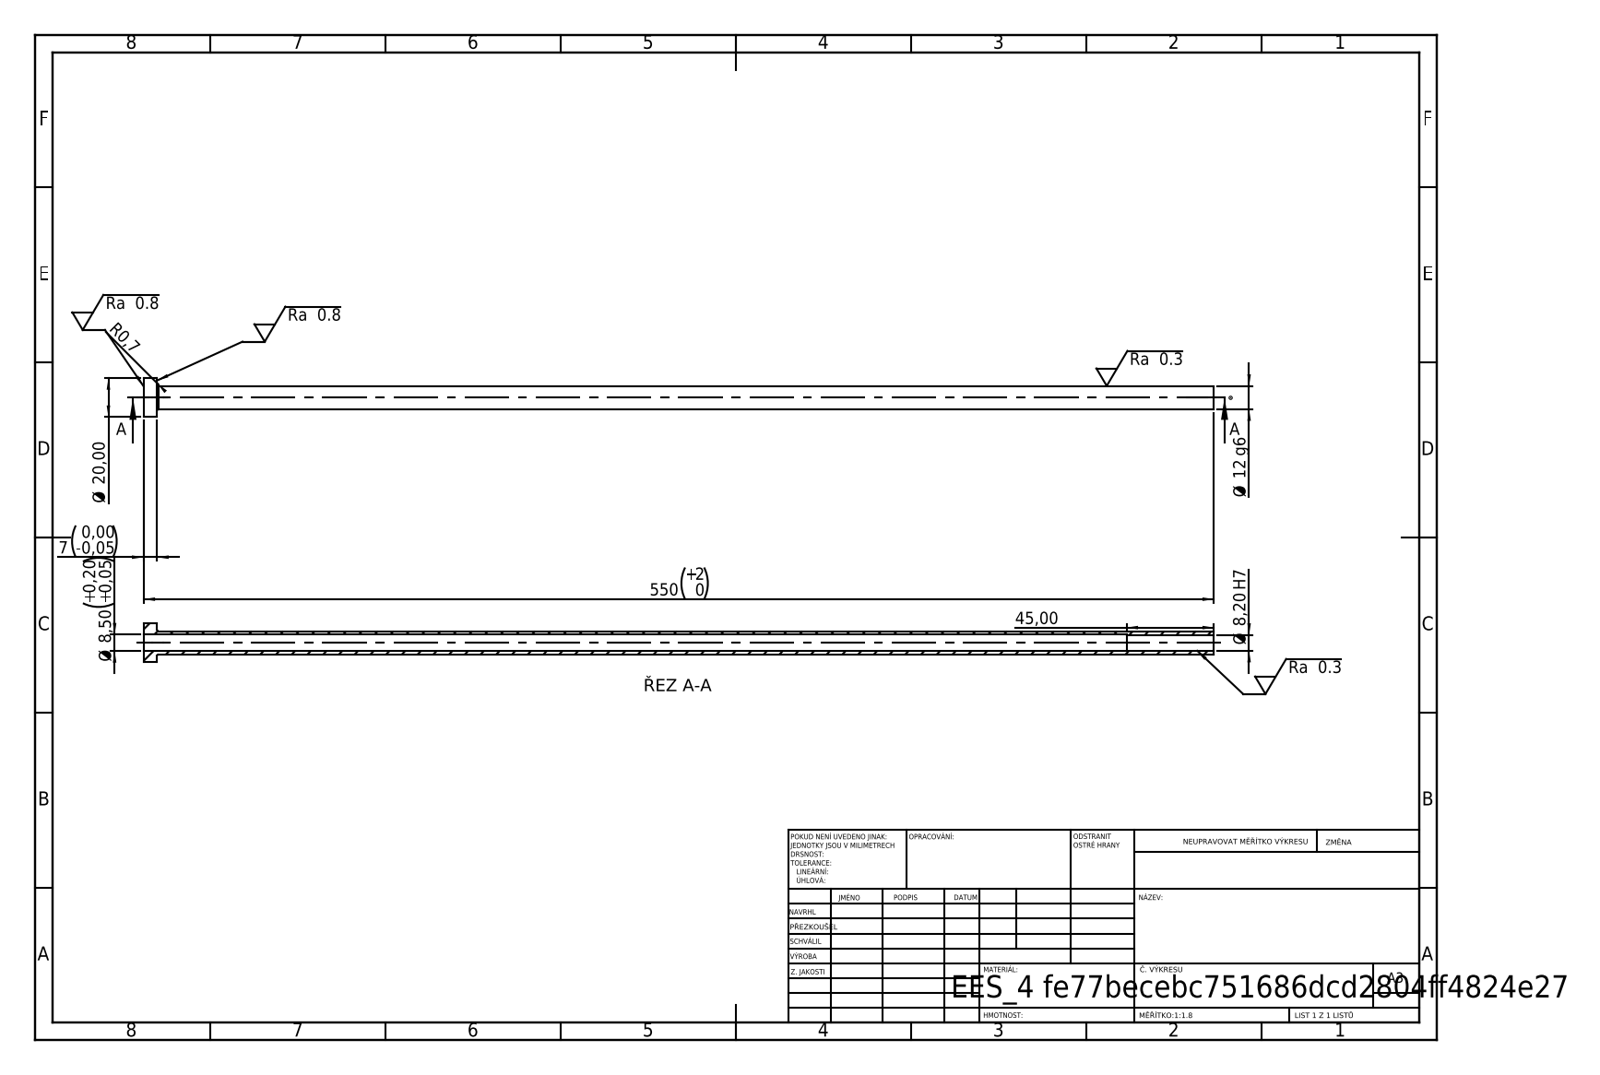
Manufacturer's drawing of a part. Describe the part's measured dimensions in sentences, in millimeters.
Its 3-D file was written by "SolidWorks 2019 (CONFIG_CONTROL_DESIGN)". It is 1 solid with 14 faces: 4 planar, 8 cylindrical and 2 other. Overall it measures 550 by 20 by 20 millimeters. Its volume is 32 582 cubic millimeters and its surface area 36 067 square millimeters. Round holes: 1 of diameter 8.2, 1 of diameter 8.5. Round bosses or shafts: 1 of diameter 20, 1 of diameter 12. The main face-to-face distances are 7, 550, 543, 505, 498, 45.
